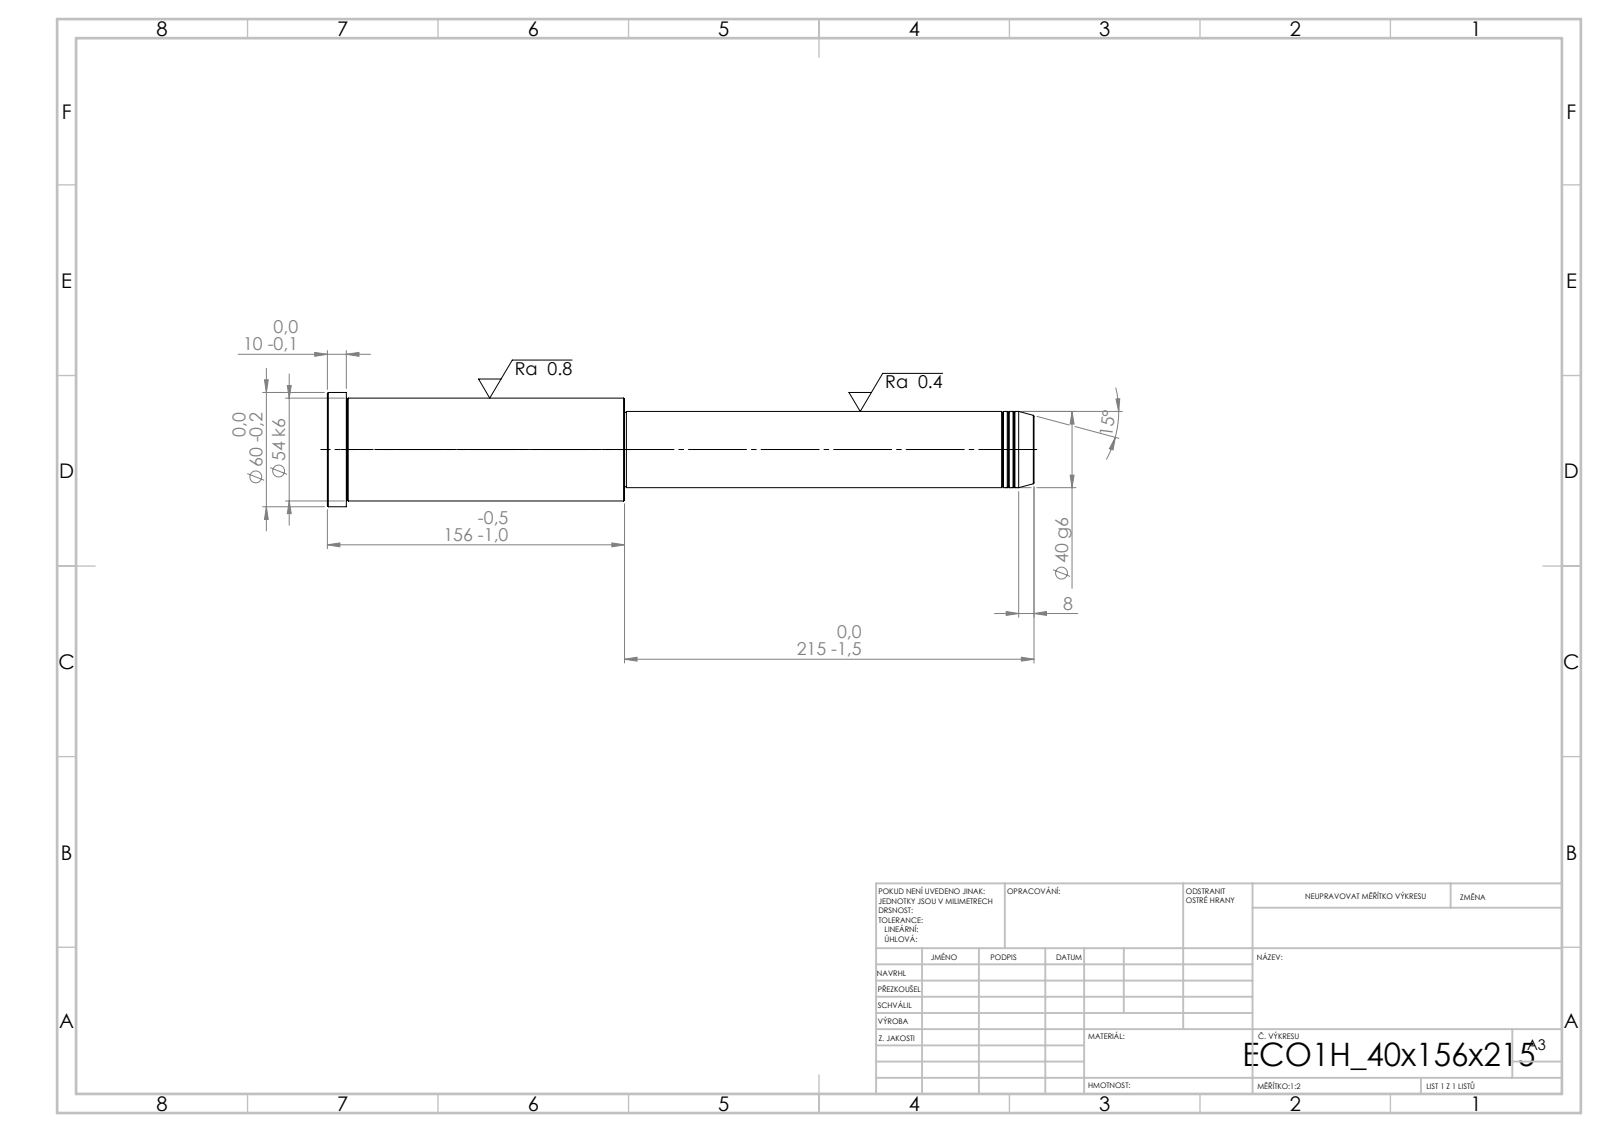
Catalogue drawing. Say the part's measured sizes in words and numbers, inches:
Its 3-D file was written by "SolidWorks 2019 (CONFIG_CONTROL_DESIGN)". It is 1 solid with 43 faces: 5 planar, 14 cylindrical and 24 other. Overall it measures 14.606 by 2.362 by 2.362 inches. Its volume is 38.53 cubic inches and its surface area 92 square inches. Round bosses or shafts: 1 of diameter 2.362, 1 of diameter 2.126, 1 of diameter 1.575, 1 of diameter 1.535. The main face-to-face distances are 6.142, 8.465, 14.606, 14.213, 5.748, 0.394, 8.425, 0.039, 5.787, 6.181.
